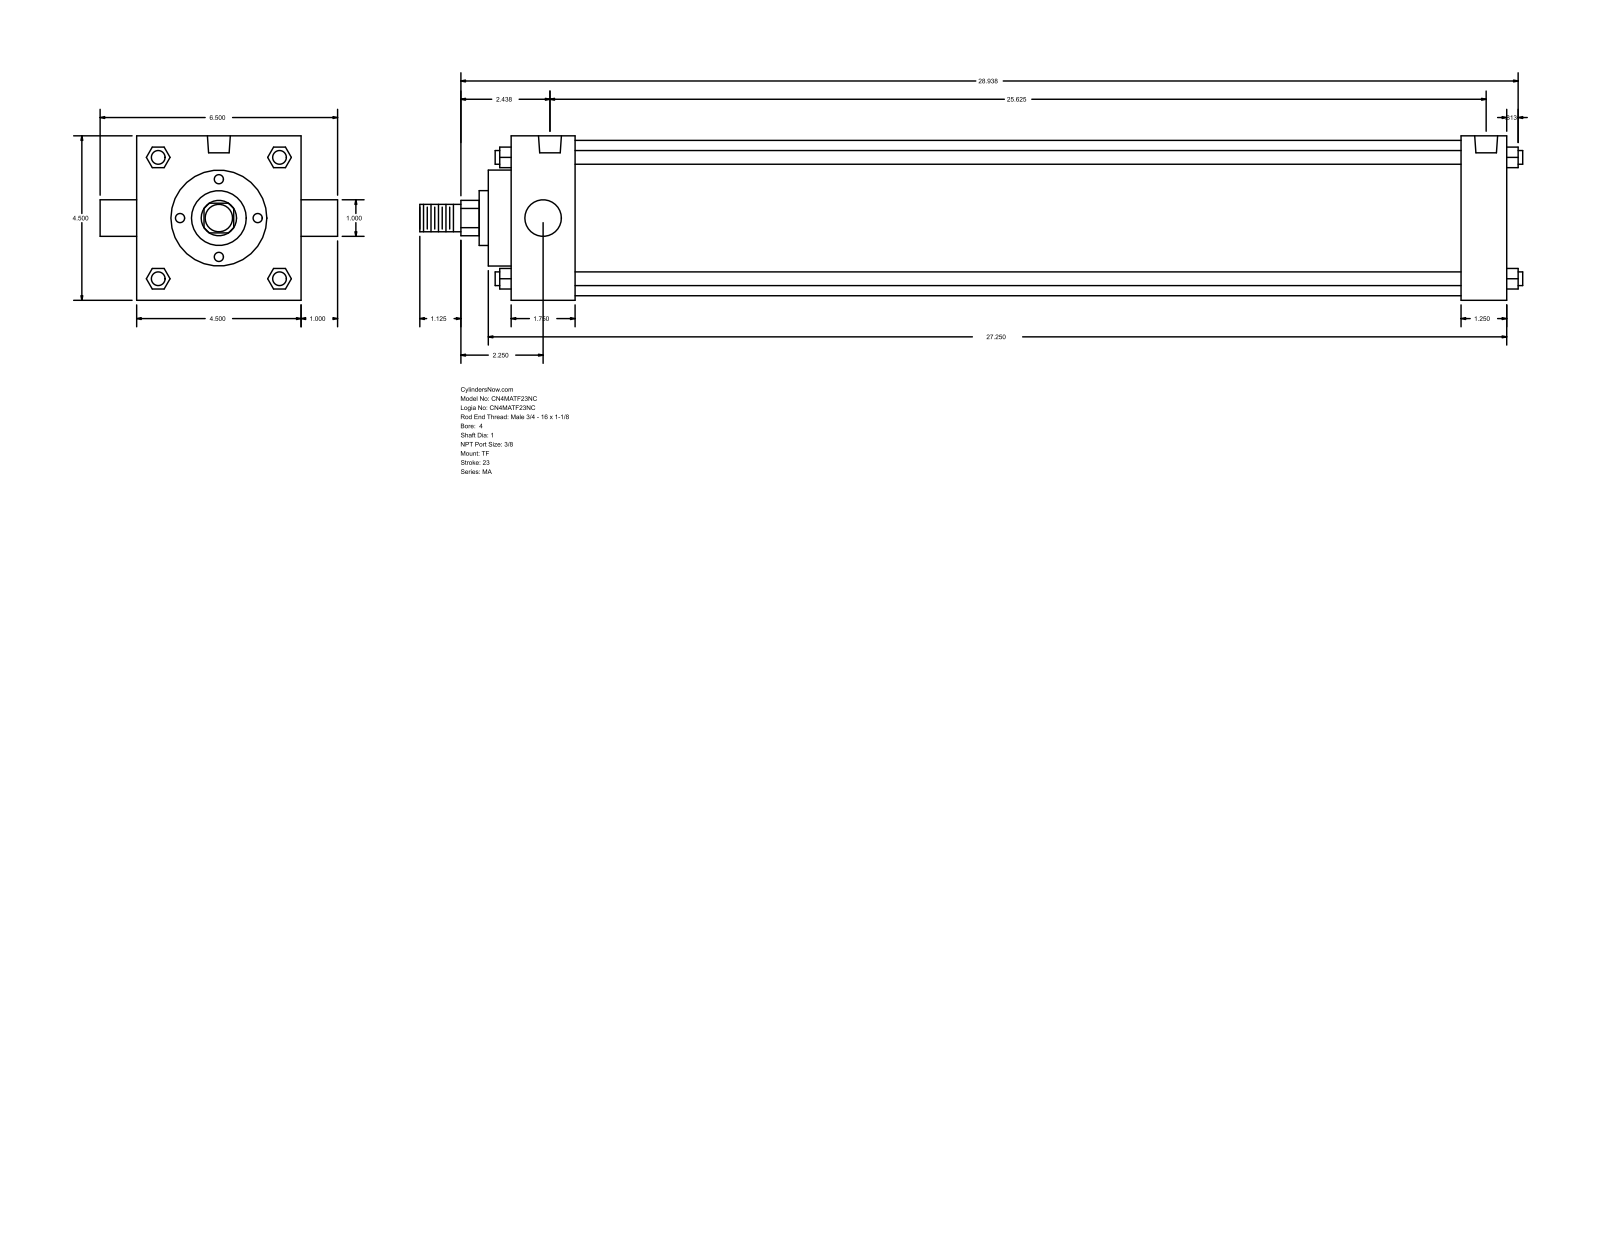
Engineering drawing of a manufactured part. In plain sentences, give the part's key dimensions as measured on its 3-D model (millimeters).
The part is named "MA_TF__0400_1". Its 3-D file was written by "GSSL Pune (CONFIG_CONTROL_DESIGN)". It is 0 solids with 122 faces: 93 planar, 29 cylindrical and 0 other. Overall it measures 766.76 by 165.1 by 114.3 millimeters. Round holes: 3 of diameter 11.11, 2 of diameter 15.93. Round bosses or shafts: 4 of diameter 9.53, 2 of diameter 25.4, 1 of diameter 107.95, 1 of diameter 66.67, 1 of diameter 38.1, 1 of diameter 19.05. Partial cylindrical surfaces (rounded edges, fillets, slot ends): 1 of radius 12.29. The main face-to-face distances are 114.3, 692.16, 660.41, 31.75, 44.46, 615.95, 647.7, 15.87, 60.33, 676.28. The hole center spacings are 4.76, 4.77, 641.35, 646.11, 646.12, 650.88.
